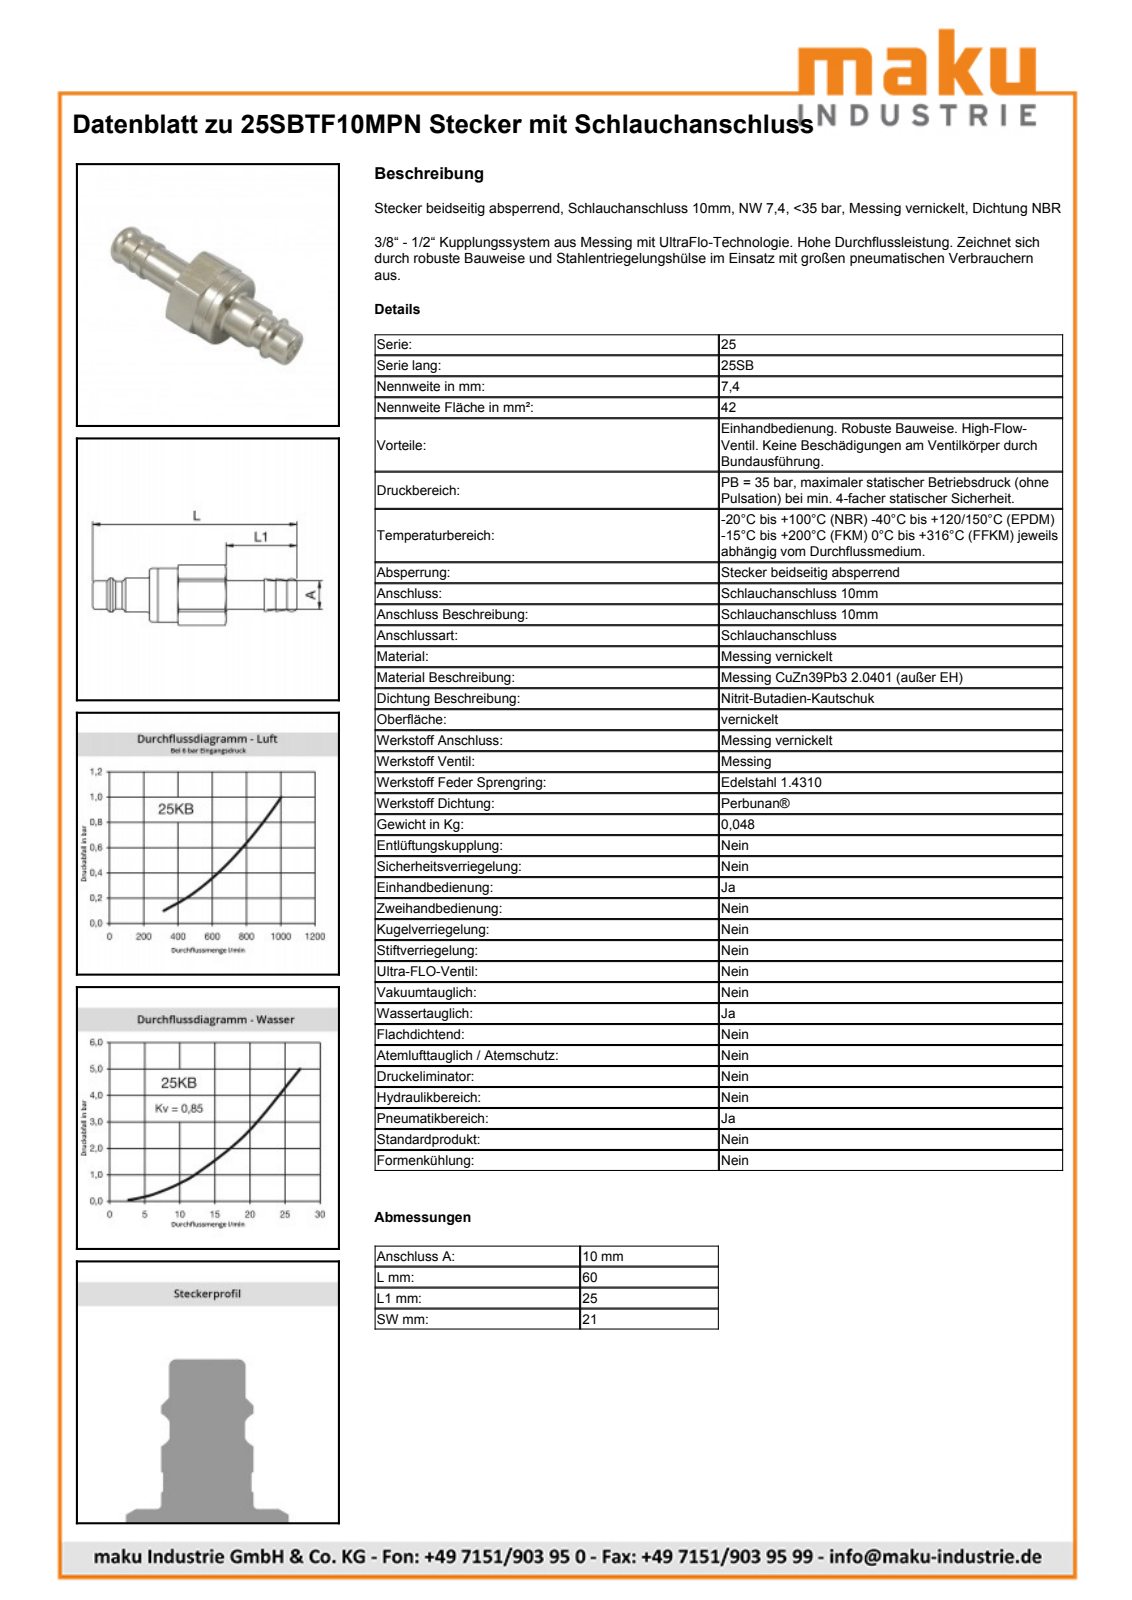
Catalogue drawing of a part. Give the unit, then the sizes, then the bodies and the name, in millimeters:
Units: millimetres
Overall size (bounding box): 60 × 23.57 × 22.38
Round holes (diameter × count): ⌀17 ×1
Round bosses / shafts (diameter × count): ⌀21 ×1, ⌀16.5 ×1, ⌀12 ×1, ⌀10.1 ×1, ⌀10 ×1, ⌀9.75 ×1
Partial cylindrical surfaces — rounded edges, fillets, slot ends (radius × count): R11.85 ×1
Main face-to-face distances: 21, 15, 20.98, 40, 25, 20, 35, 60, 23, 3
Volume: 9 533 mm³ · Surface area: 3 512 mm²
Bodies: 1 solid, 58 faces (17 planar, 14 cylindrical, 27 other)
Part name (STEP PRODUCT): D109052
STEP written by: Autodesk Inventor 2013 (AUTOMOTIVE_DESIGN)
